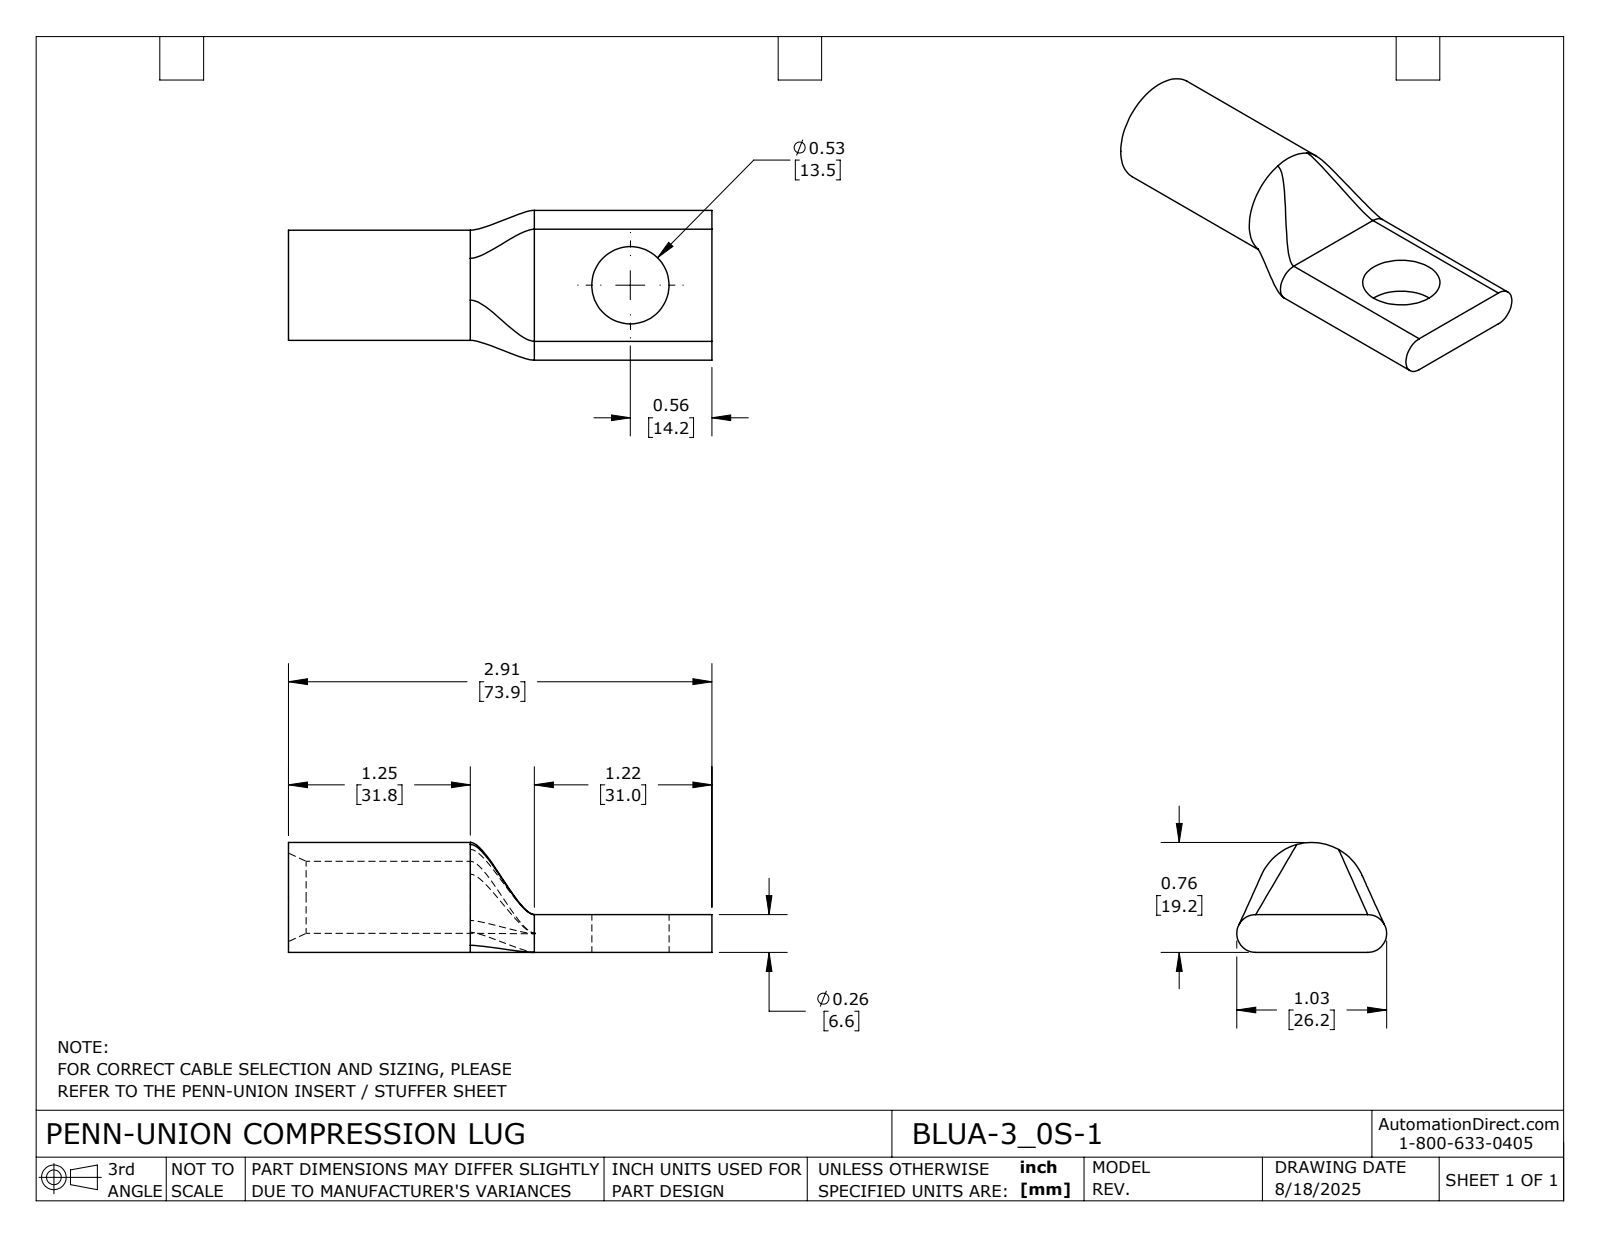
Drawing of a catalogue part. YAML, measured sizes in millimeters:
part_name: "BLUA-3_0S-1"
step_written_by: "SolidWorks 2024 (CONFIG_CONTROL_DESIGN)"
units: millimeters
bodies: {solids: 1, faces: 24, planar: 5, cylindrical: 9, other: 10}
overall_size: [73.9, 26.2, 19.2]
volume: 11100
surface_area: 6606
round_holes:
  - {diameter: 12.6, count: 1}
  - {diameter: 13.5, count: 1}
round_bosses_or_shafts:
  - {diameter: 19.2, count: 1}
partial_cylinders:
  - {radius: 3.3, count: 2}
face_to_face_distances: [6.6, 73.9, 42.9, 31]
